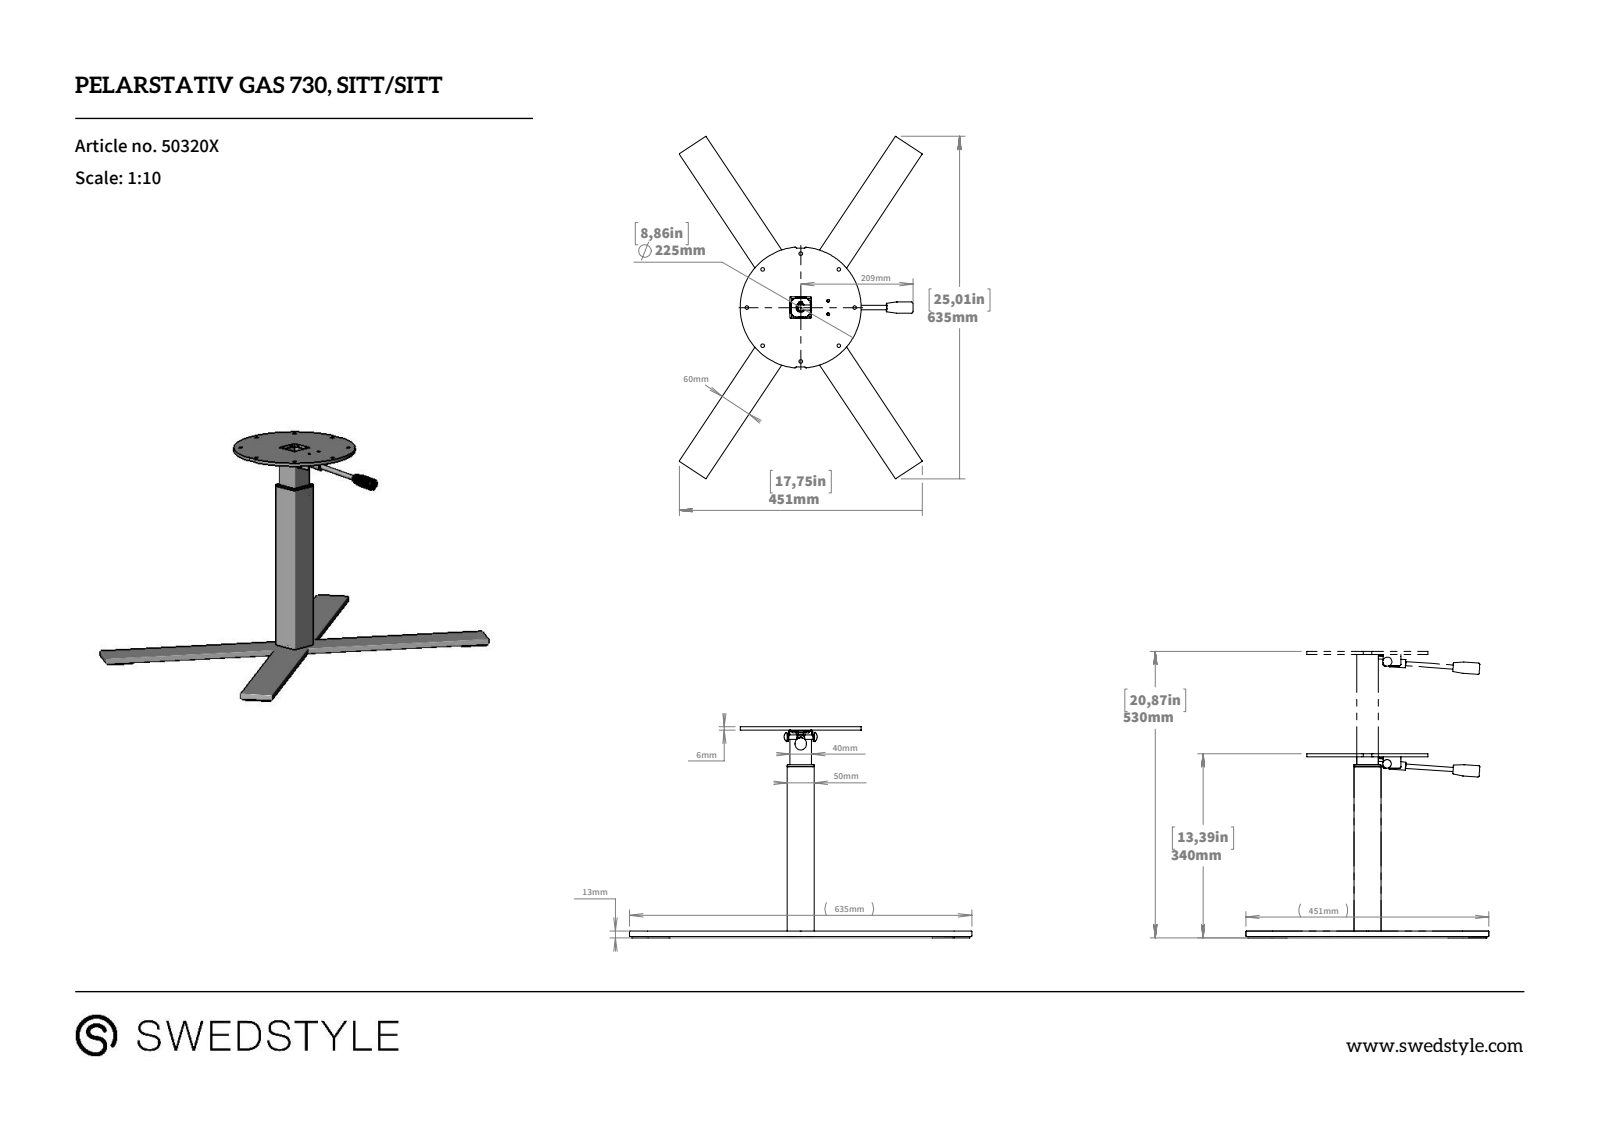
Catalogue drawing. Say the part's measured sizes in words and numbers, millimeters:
The part is named "50320x_Pelarstativ 730, spak, Sitt_Sitt". Its 3-D file was written by "SolidWorks 2017 (CONFIG_CONTROL_DESIGN)". It is 0 solids with 314 faces: 133 planar, 126 cylindrical and 55 other. Overall it measures 635.23 by 450.63 by 391.5 millimeters. Round holes: 12 of diameter 6.6, 4 of diameter 3.4, 2 of diameter 5, 1 of diameter 1.7, 1 of diameter 9. Round bosses or shafts: 2 of diameter 8, 1 of diameter 225, 1 of diameter 21, 1 of diameter 15. Partial cylindrical surfaces (rounded edges, fillets, slot ends): 26 of radius 1, 22 of radius 2, 8 of radius 2.5, 4 of radius 0.5, 4 of radius 2.75, 4 of radius 3, 2 of radius 4, 1 of radius 6. The main face-to-face distances are 10, 2, 5, 45, 43, 7, 38, 389, 379, 6. The hole center spacings are 76.54, 84.72, 100, 102.85, 118.23, 141.42, 184.78, 24.04.
